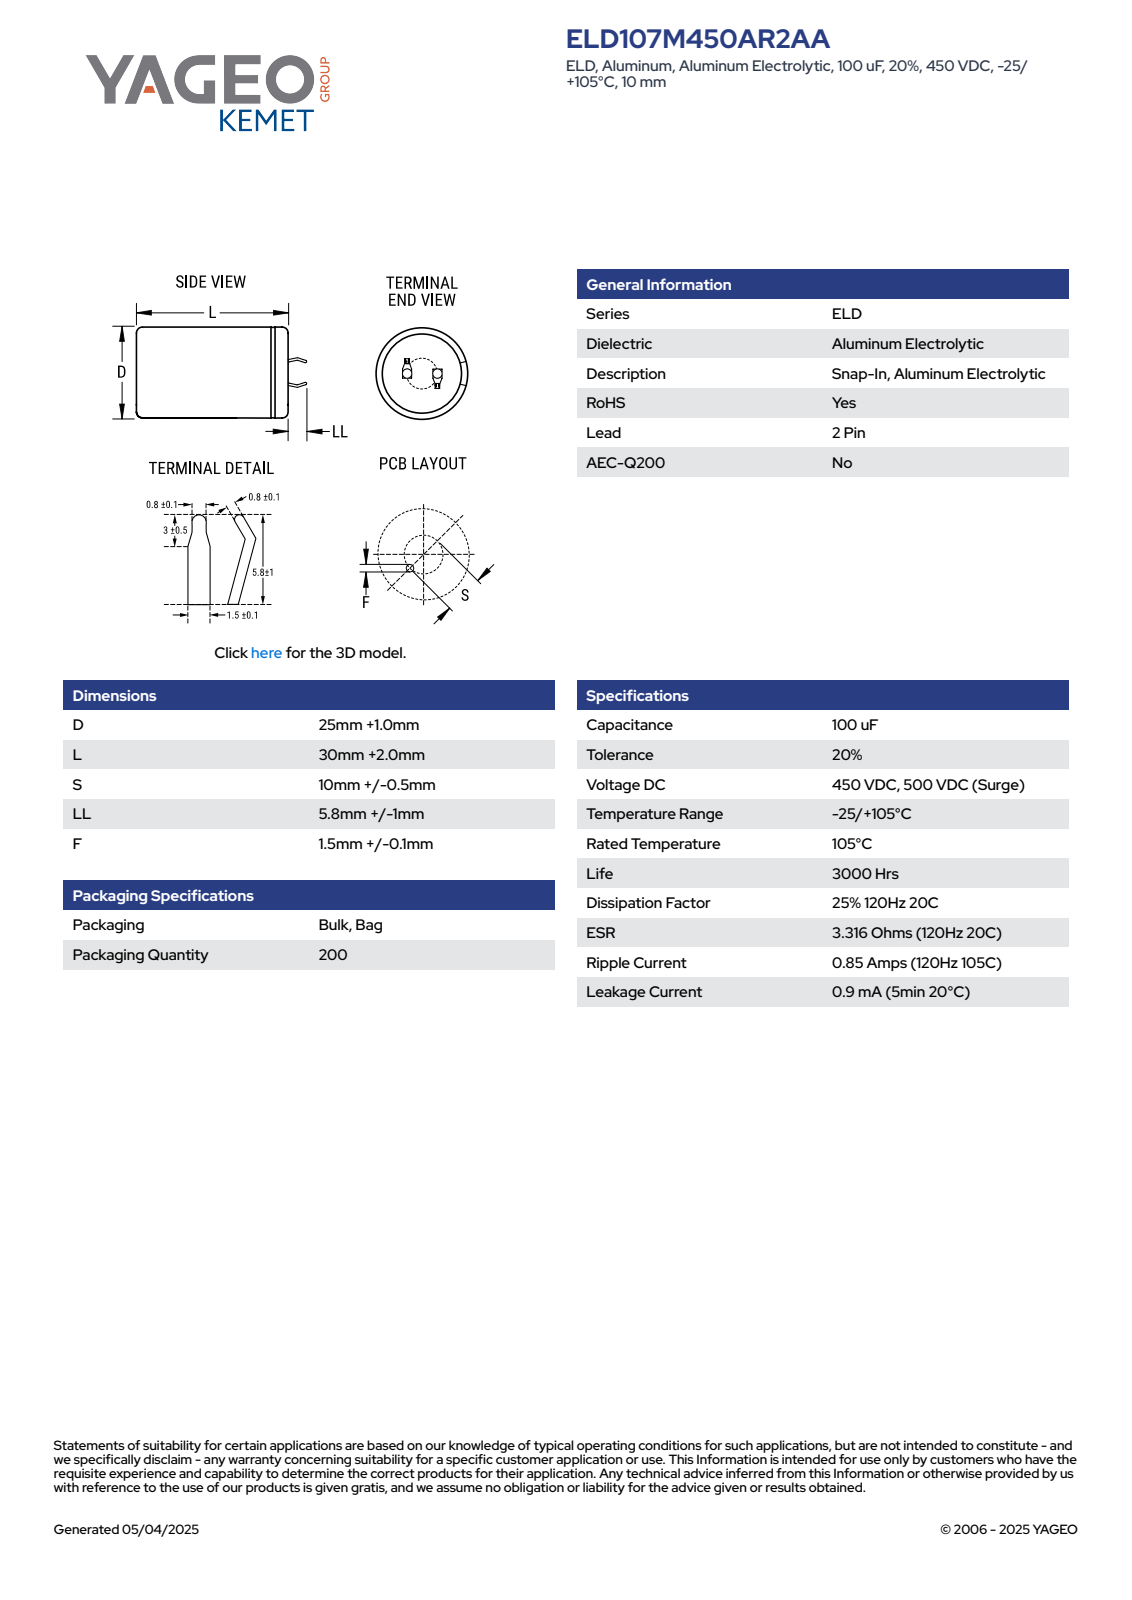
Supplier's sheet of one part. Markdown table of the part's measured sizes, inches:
| quantity | value |
| --- | --- |
| part name | CARS_K2P_25X30_D26L32S10LL6.8F1.6 |
| STEP written by | SolidWorks 2014 (AUTOMOTIVE_DESIGN) |
| units | inches |
| bodies | 1 solid, 100 faces (52 planar, 9 cylindrical, 39 other) |
| overall size | 1.527 × 1.024 × 1.024 |
| volume | 1.025 in³ |
| surface area | 5.726 in² |
| round holes (diameter × count) | 0.906 × 1 |
| round bosses / shafts (diameter × count) | 1.024 × 1 |
| partial cylindrical surfaces (radius × count) | 0.511 × 1 |
| main face-to-face distances | 1.259, 0.024, 1.279, 0.02, 0.279, 0.3, 0.03, 0.053, 0.302, 0.255 |
